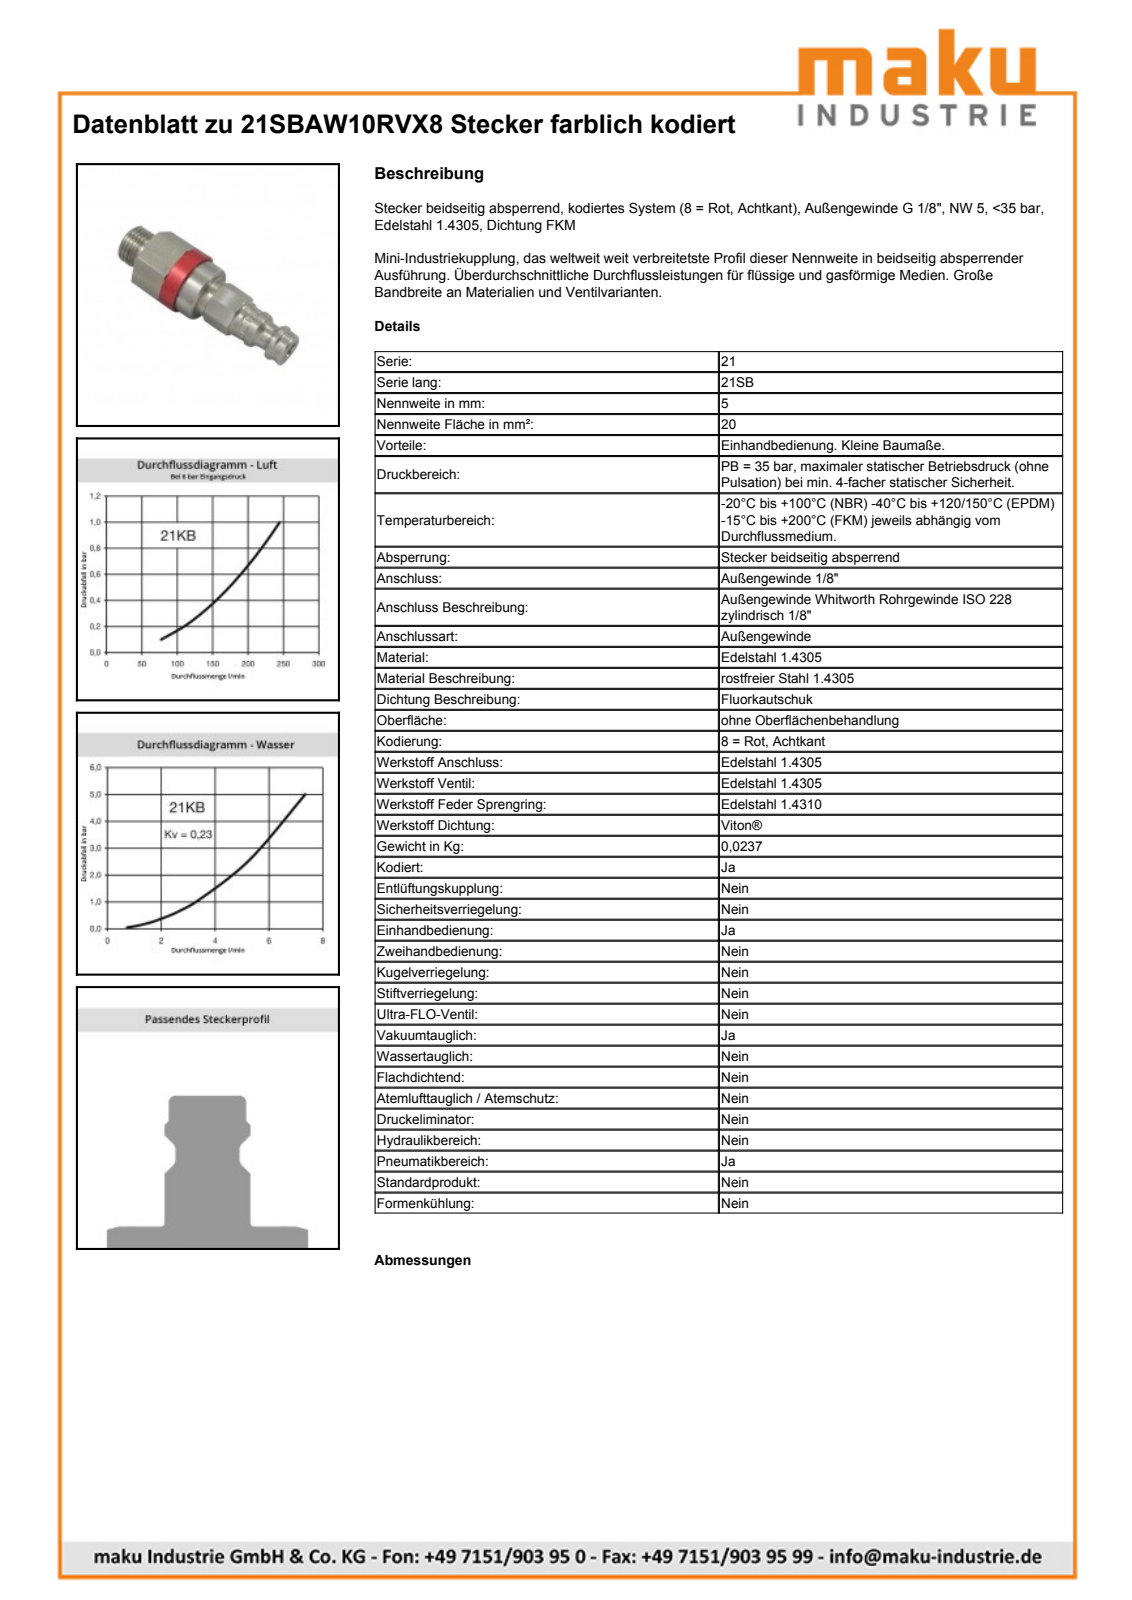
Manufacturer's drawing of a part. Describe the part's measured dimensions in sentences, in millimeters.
The part is named "21SBAW10RVX8; GSA21W10RXX; SOX21SBXRXX8; DHX21XXXAXX_02". Its 3-D file was written by "Autodesk Inventor 2017 (AUTOMOTIVE_DESIGN)". It is 3 solids with 271 faces: 75 planar, 50 cylindrical and 146 other. Overall it measures 47.3 by 15.8 by 15.5 millimeters. Its volume is 5 371 cubic millimeters and its surface area 2 947 square millimeters. Round holes: 1 of diameter 13.85, 1 of diameter 14.05. Round bosses or shafts: 1 of diameter 15.5, 1 of diameter 14, 1 of diameter 12, 1 of diameter 10.85, 1 of diameter 9.73, 1 of diameter 9.7, 1 of diameter 9, 1 of diameter 8.5. Partial cylindrical surfaces (rounded edges, fillets, slot ends): 1 of radius 4.24, 1 of radius 5.35, 1 of radius 7.9. The main face-to-face distances are 14, 4.7, 10, 8.3, 13, 7, 15.3, 20, 23.8, 16.8.
